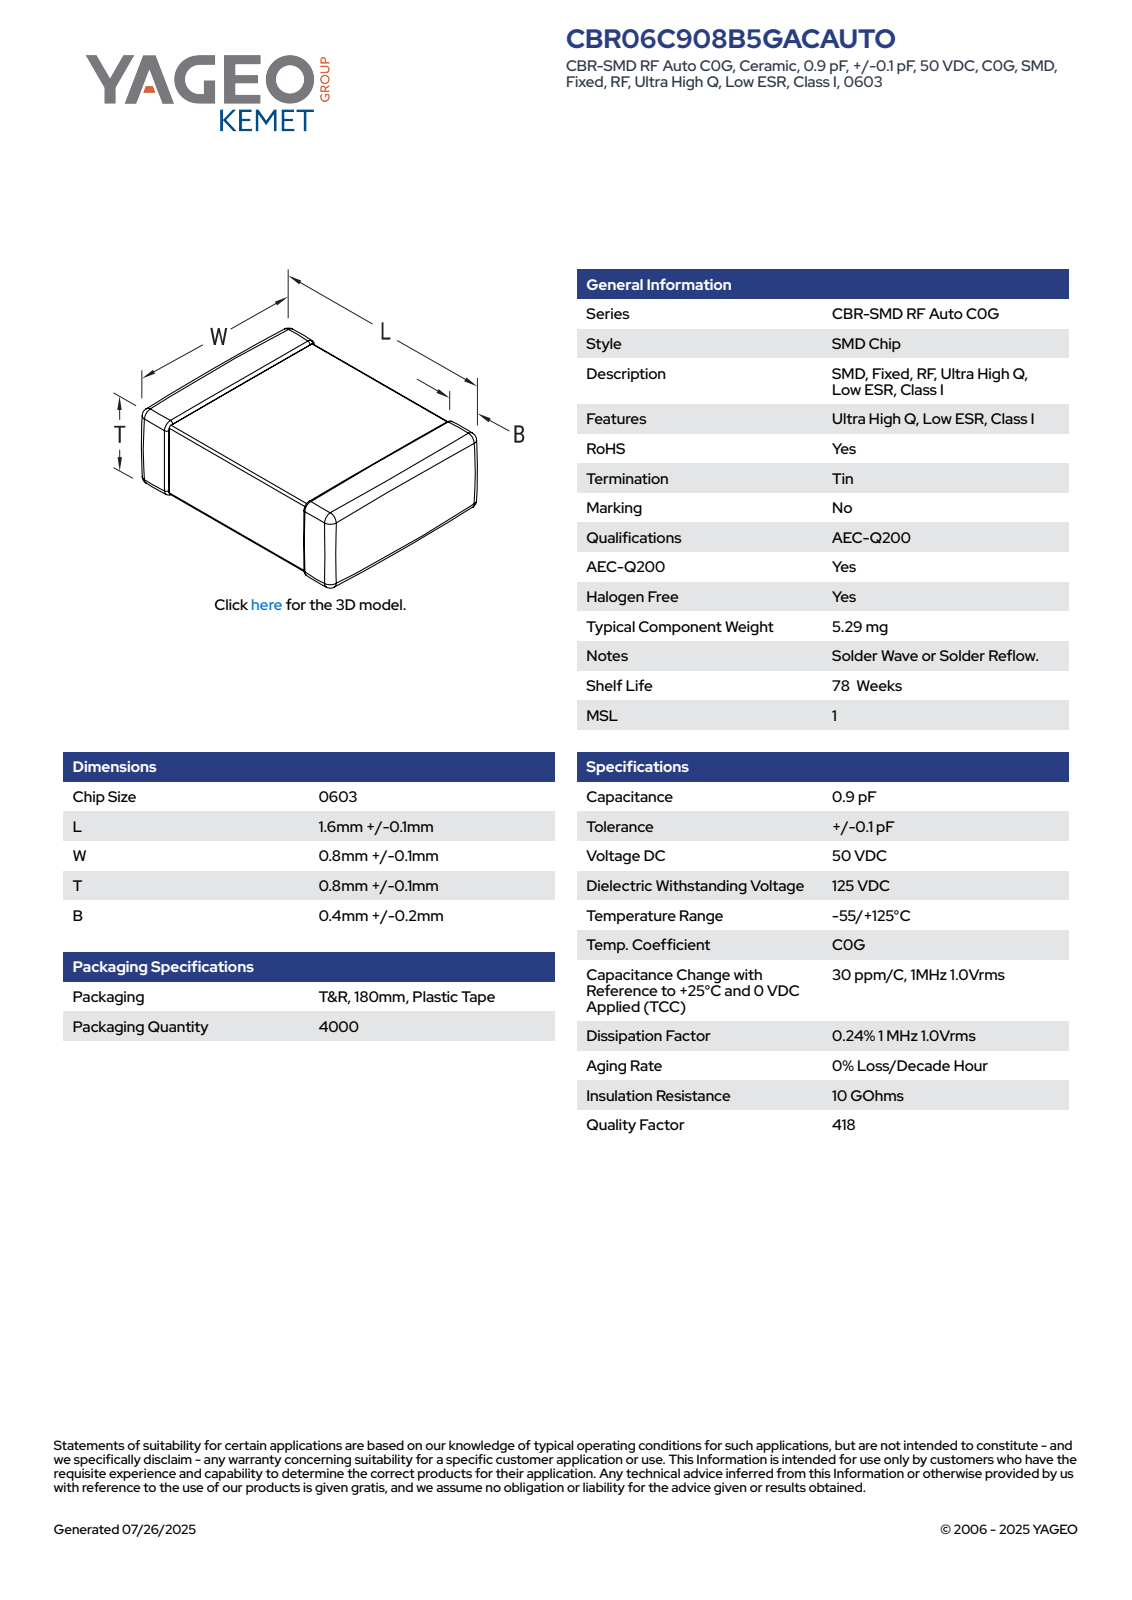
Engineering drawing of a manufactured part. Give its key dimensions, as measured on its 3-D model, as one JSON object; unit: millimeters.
{"part_name": "CCS_CCSTDNOS_0603_L1.7W0.9T0.9B0.6", "step_written_by": "SolidWorks 2021 (AUTOMOTIVE_DESIGN)", "units": "millimeters", "bodies": {"solids": 4, "faces": 129, "planar": 71, "cylindrical": 42, "other": 16}, "overall_size": [1.7, 0.9, 0.9], "volume_mm3": 1, "surface_area_mm2": 8, "face_to_face_distances": [0.9, 0.88, 0.86, 1.7, 0.89, 0.87, 0.38, 0.5, 0.4, 0.48]}
